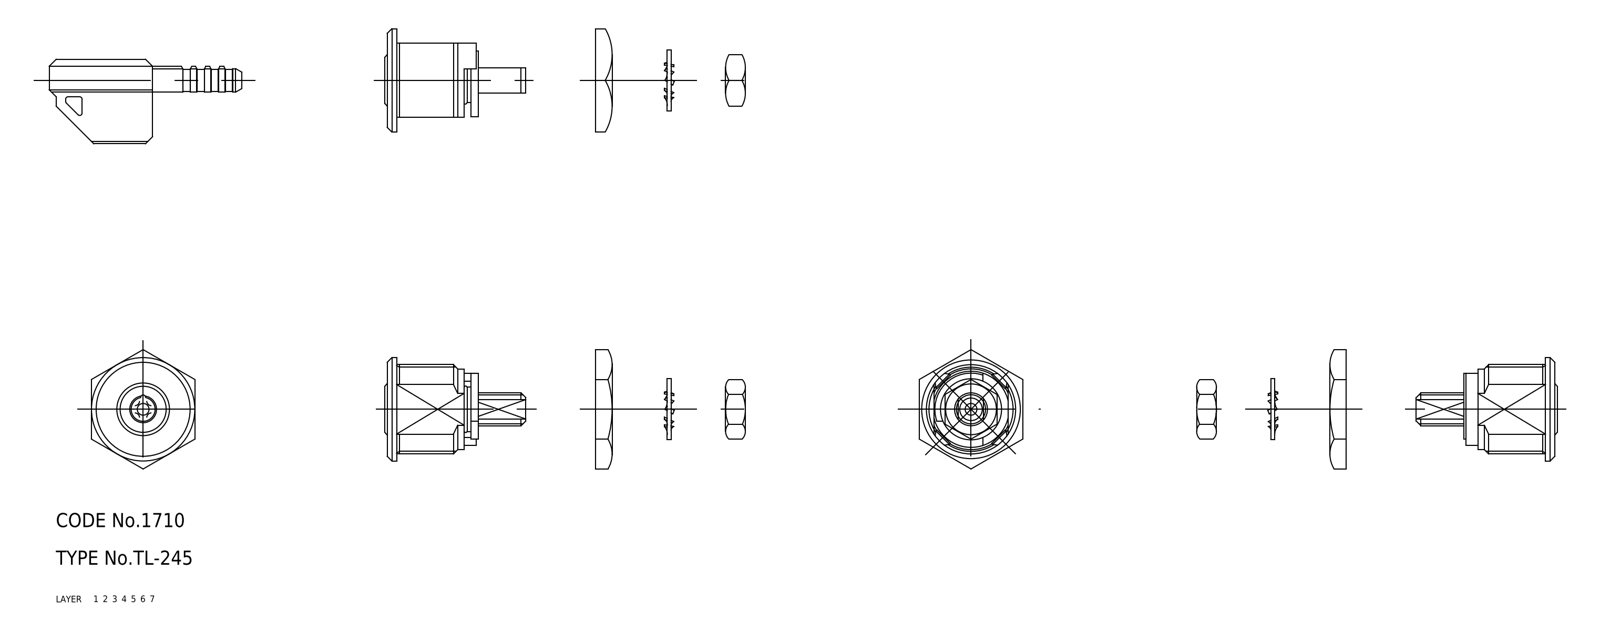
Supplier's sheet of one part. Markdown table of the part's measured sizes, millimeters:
| quantity | value |
| --- | --- |
| part name | washer; nut_B; nut_A; lock (+3 more) |
| STEP written by | CADfix (AUTOMOTIVE_DESIGN) |
| units | millimeters |
| bodies | 6 solids, 169 faces (0 planar, 0 cylindrical, 169 other) |
| overall size | 91 × 26.2 × 22 |
| volume | 7 694 mm³ |
| surface area | 5 336 mm² |
